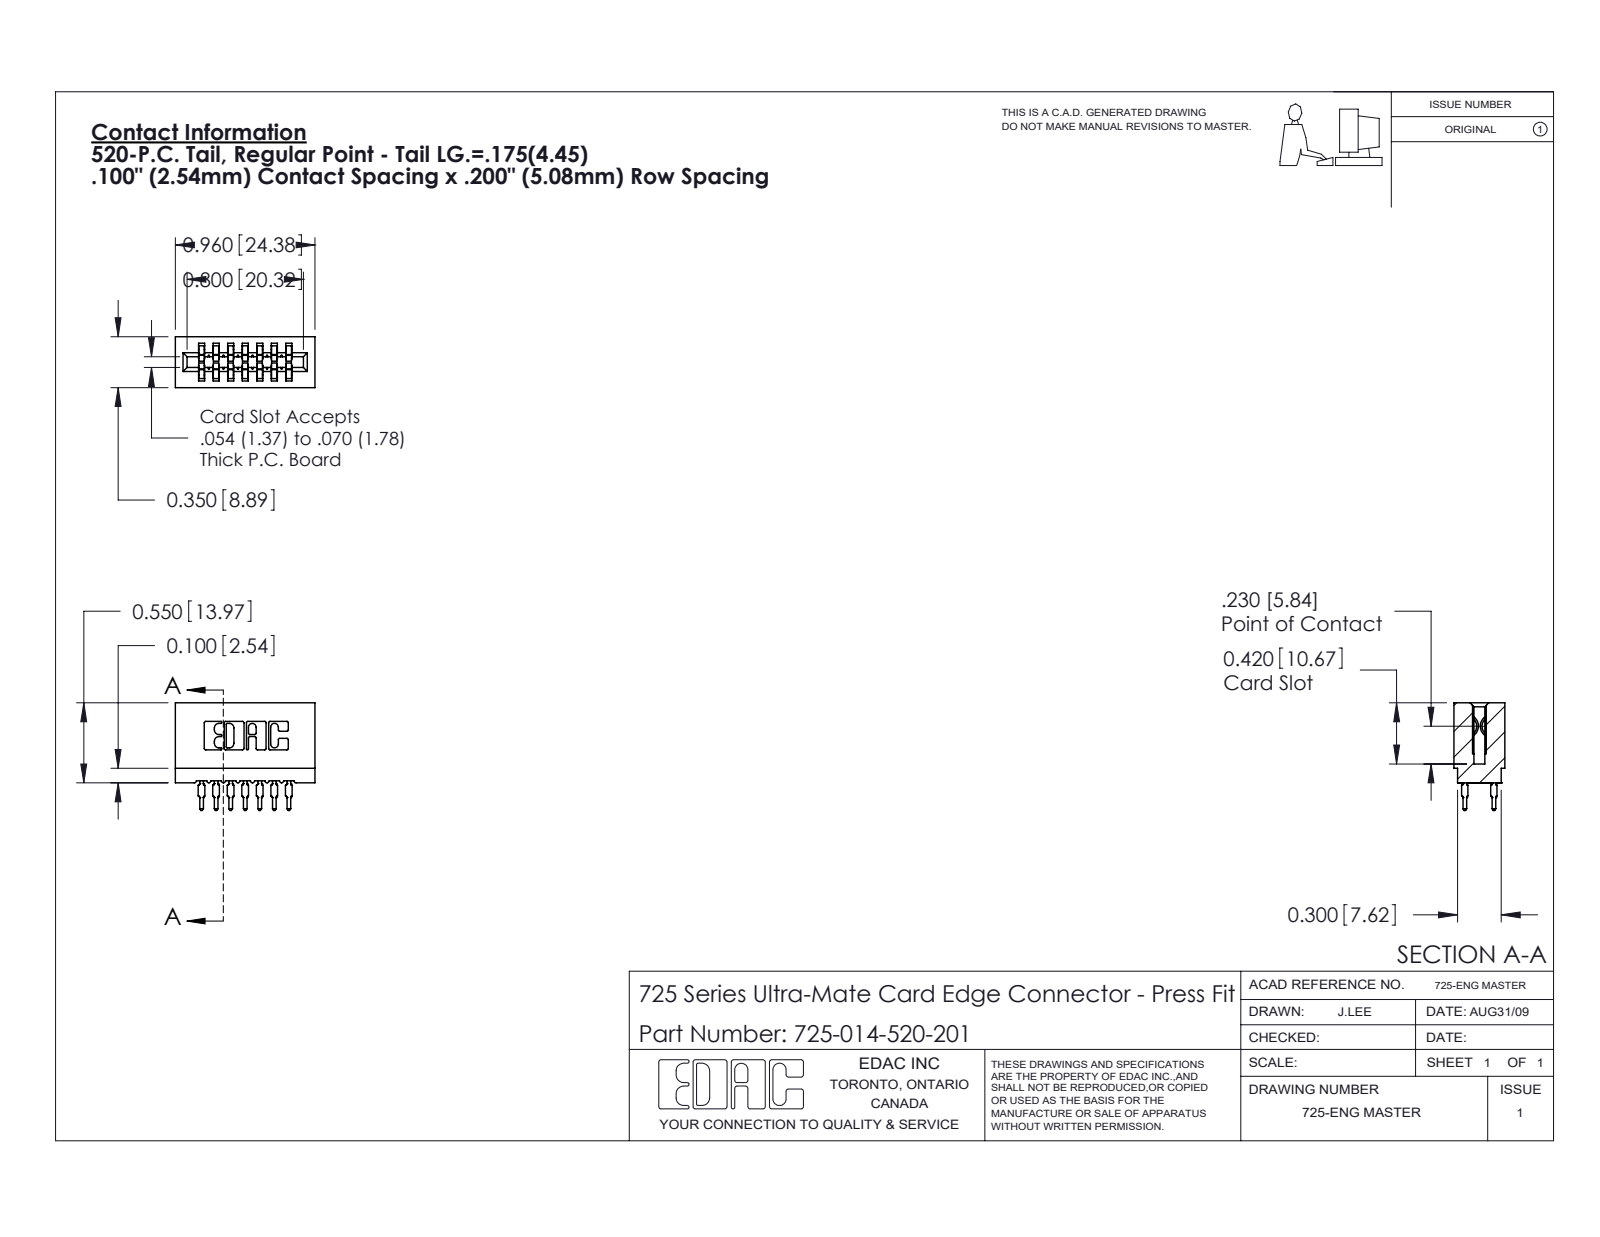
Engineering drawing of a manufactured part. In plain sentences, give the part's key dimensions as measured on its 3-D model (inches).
The part is named "725-014-520-201; 745-292-001_520; 725 Part_Insulator Option - 01". Its 3-D file was written by "SolidWorks 2020 (CONFIG_CONTROL_DESIGN)". It is 15 solids with 1348 faces: 699 planar, 285 cylindrical and 364 other. Overall it measures 0.96 by 0.741 by 0.35 inches. Its volume is 0.128 cubic inches and its surface area 5.617 square inches. Partial cylindrical surfaces (rounded edges, fillets, slot ends): 28 of radius 0.021, 22 of radius 0.01, 14 of radius 0.015, 8 of radius 0.005, 8 of radius 0.011, 6 of radius 0.007, 6 of radius 0.031, 3 of radius 0.026. The main face-to-face distances are 0.1, 0.2, 0.3, 0.042, 0.4, 0.142, 0.058, 0.242, 0.158, 0.5.
